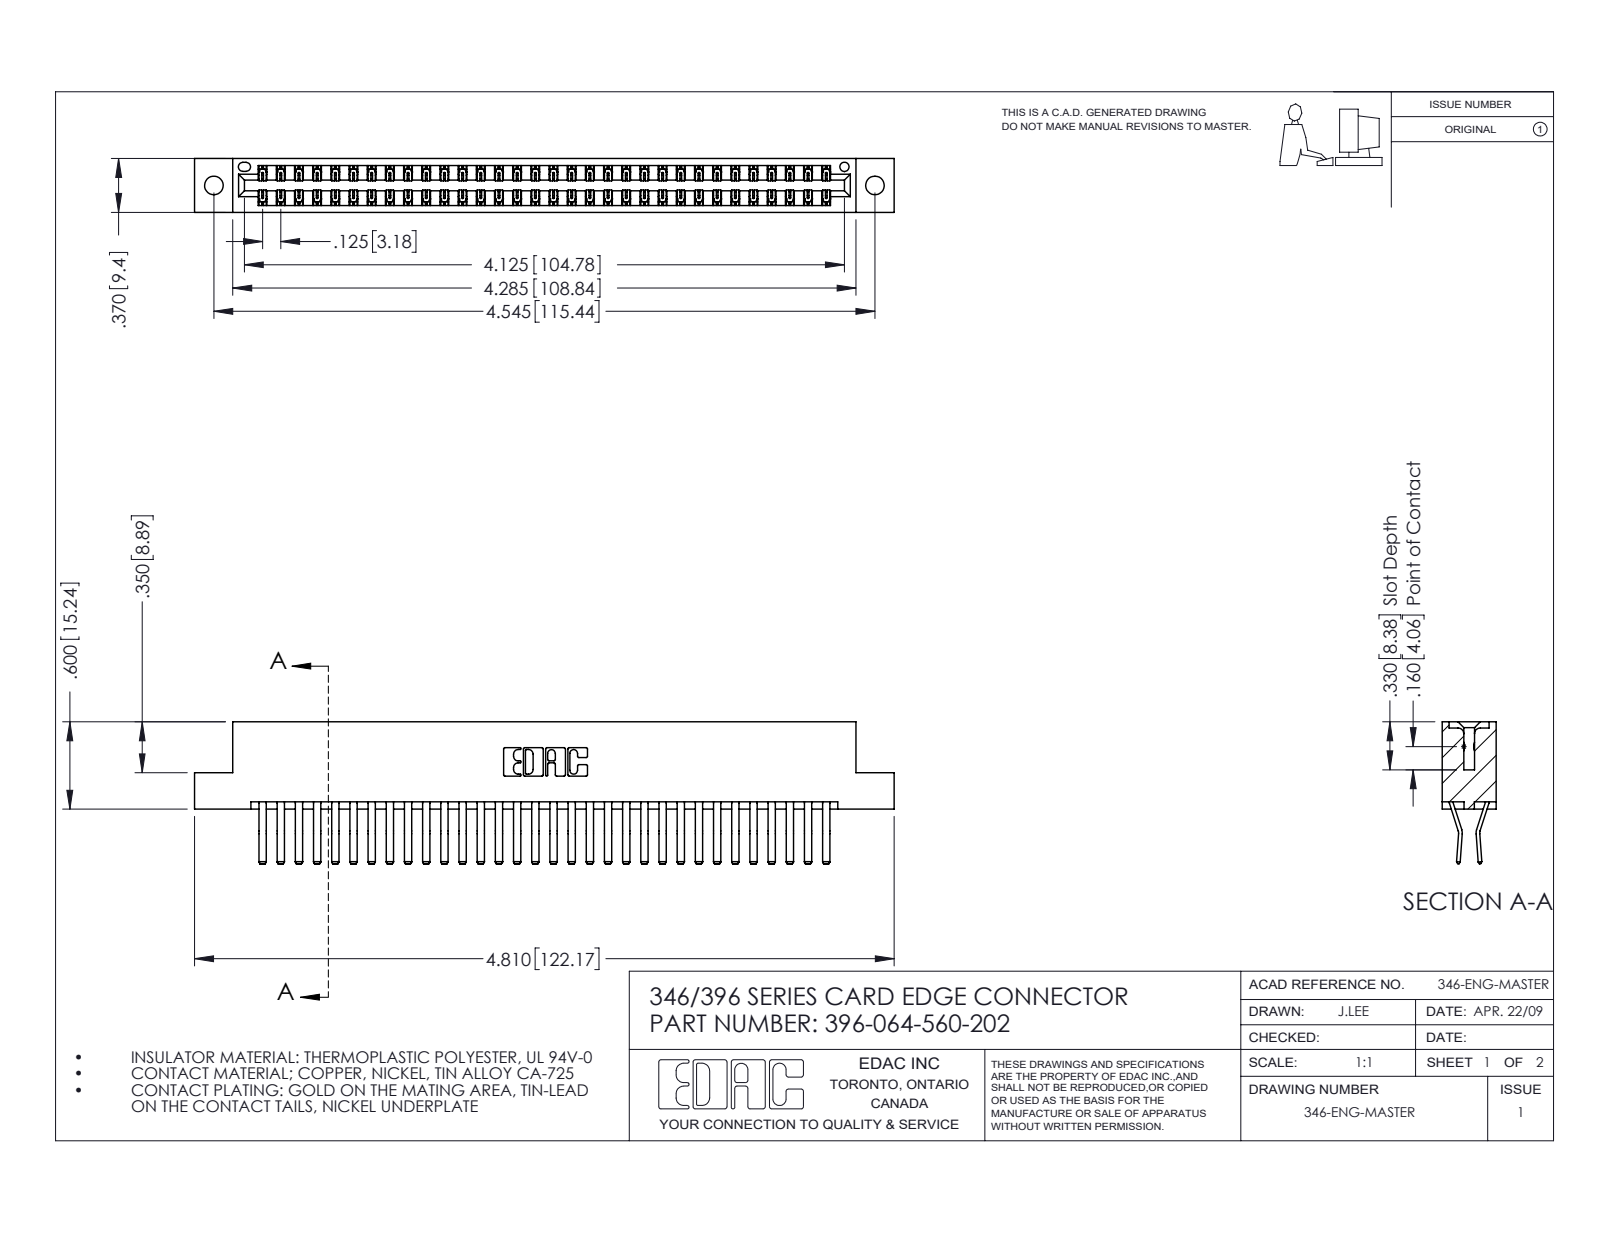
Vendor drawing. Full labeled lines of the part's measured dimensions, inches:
Part name (STEP PRODUCT): 346 Part_Flush Mounting Lugs - 0.128 Dia; 396-064-560-202; 345-292-001_560 Tail
STEP written by: SolidWorks 2016 (CONFIG_CONTROL_DESIGN)
Units: inches
Bodies: 65 solids, 3578 faces (2316 planar, 1262 cylindrical, 0 other)
Overall size (bounding box): 4.81 × 0.975 × 0.37
Volume: 0.746 in³ · Surface area: 27.11 in²
Round holes (diameter × count): ⌀0.128 ×2, ⌀0.064 ×1
Partial cylindrical surfaces — rounded edges, fillets, slot ends (radius × count): R0.006 ×96, R0.01 ×22, R0.007 ×6, R0.031 ×6, R0.026 ×3, R0.01 ×2, R0.014 ×2, R0.022 ×2
Main face-to-face distances: 0.048, 0.322, 0.37, 0.25, 0.025, 0.072, 0.298, 0.275, 0.148, 0.222
Hole centre spacings: 0.246, 4.337, 4.545
